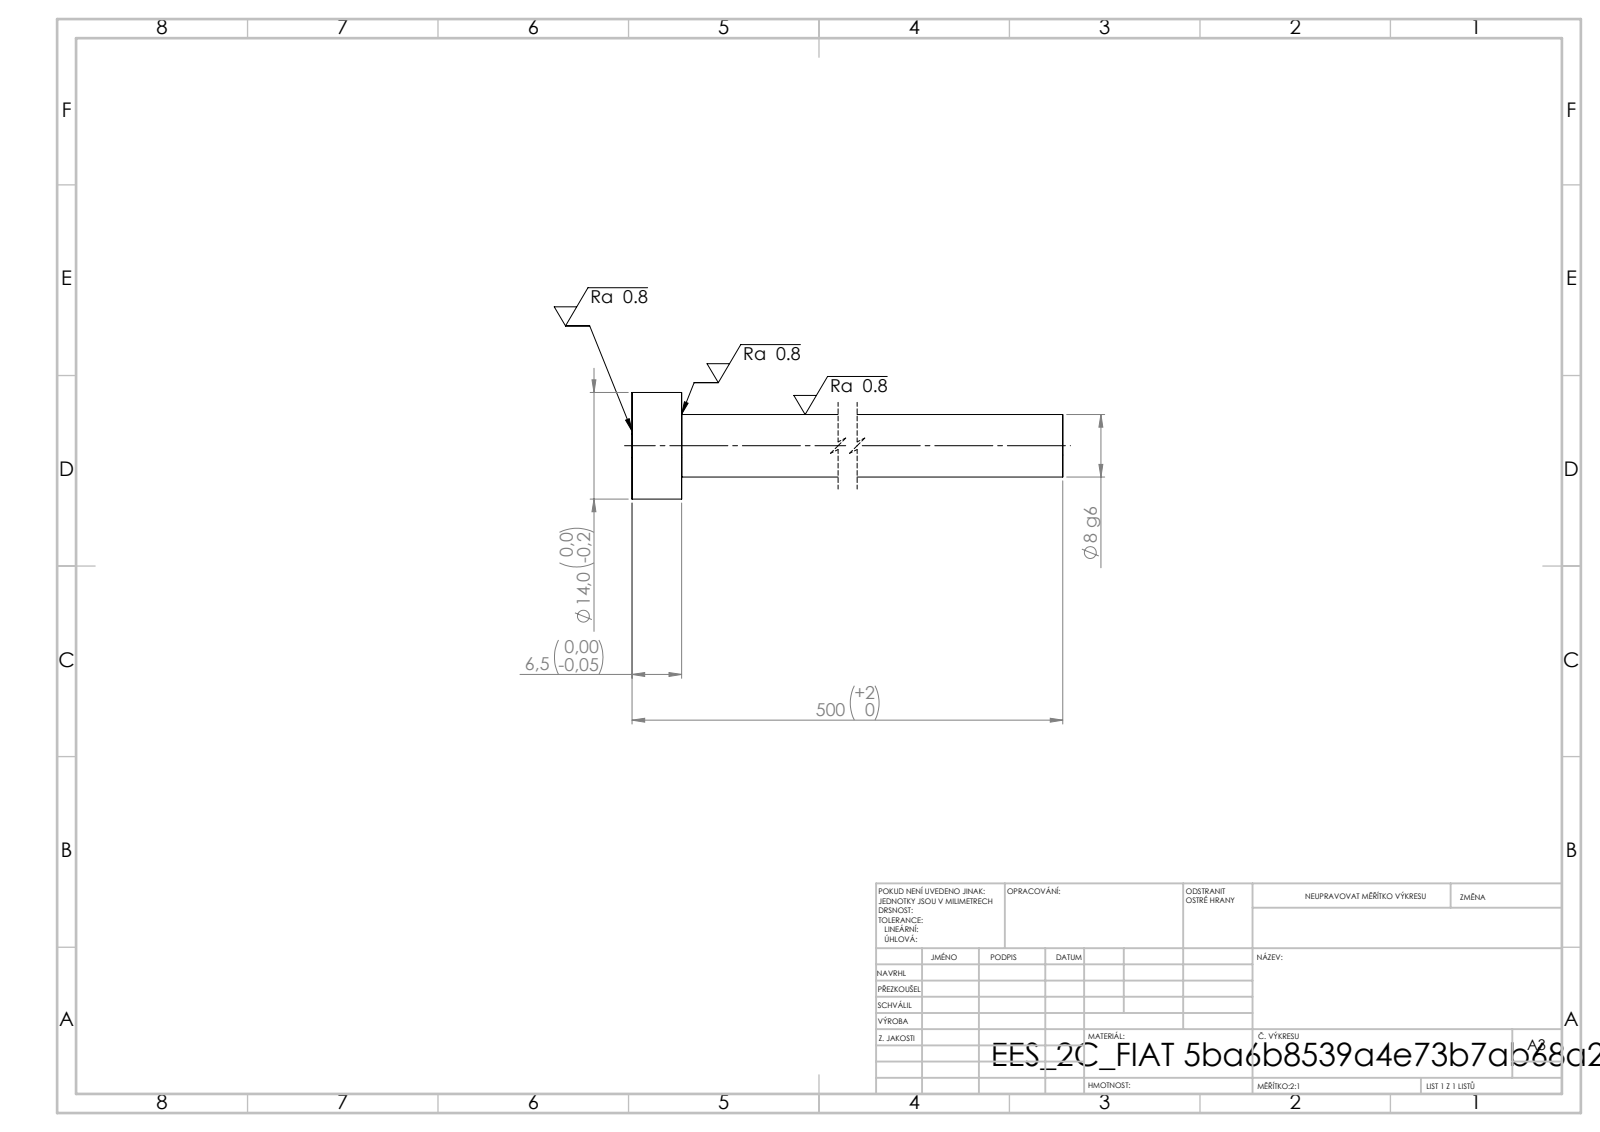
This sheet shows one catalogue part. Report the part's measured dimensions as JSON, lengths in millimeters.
{"step_written_by": "SolidWorks 2019 (CONFIG_CONTROL_DESIGN)", "units": "millimeters", "bodies": {"solids": 1, "faces": 7, "planar": 3, "cylindrical": 4, "other": 0}, "overall_size": [500, 14, 14], "volume_mm3": 27062, "surface_area_mm2": 13307, "round_bosses_or_shafts": [[14, 1], [8.2, 1]], "face_to_face_distances": [6.5, 500, 493.5]}
